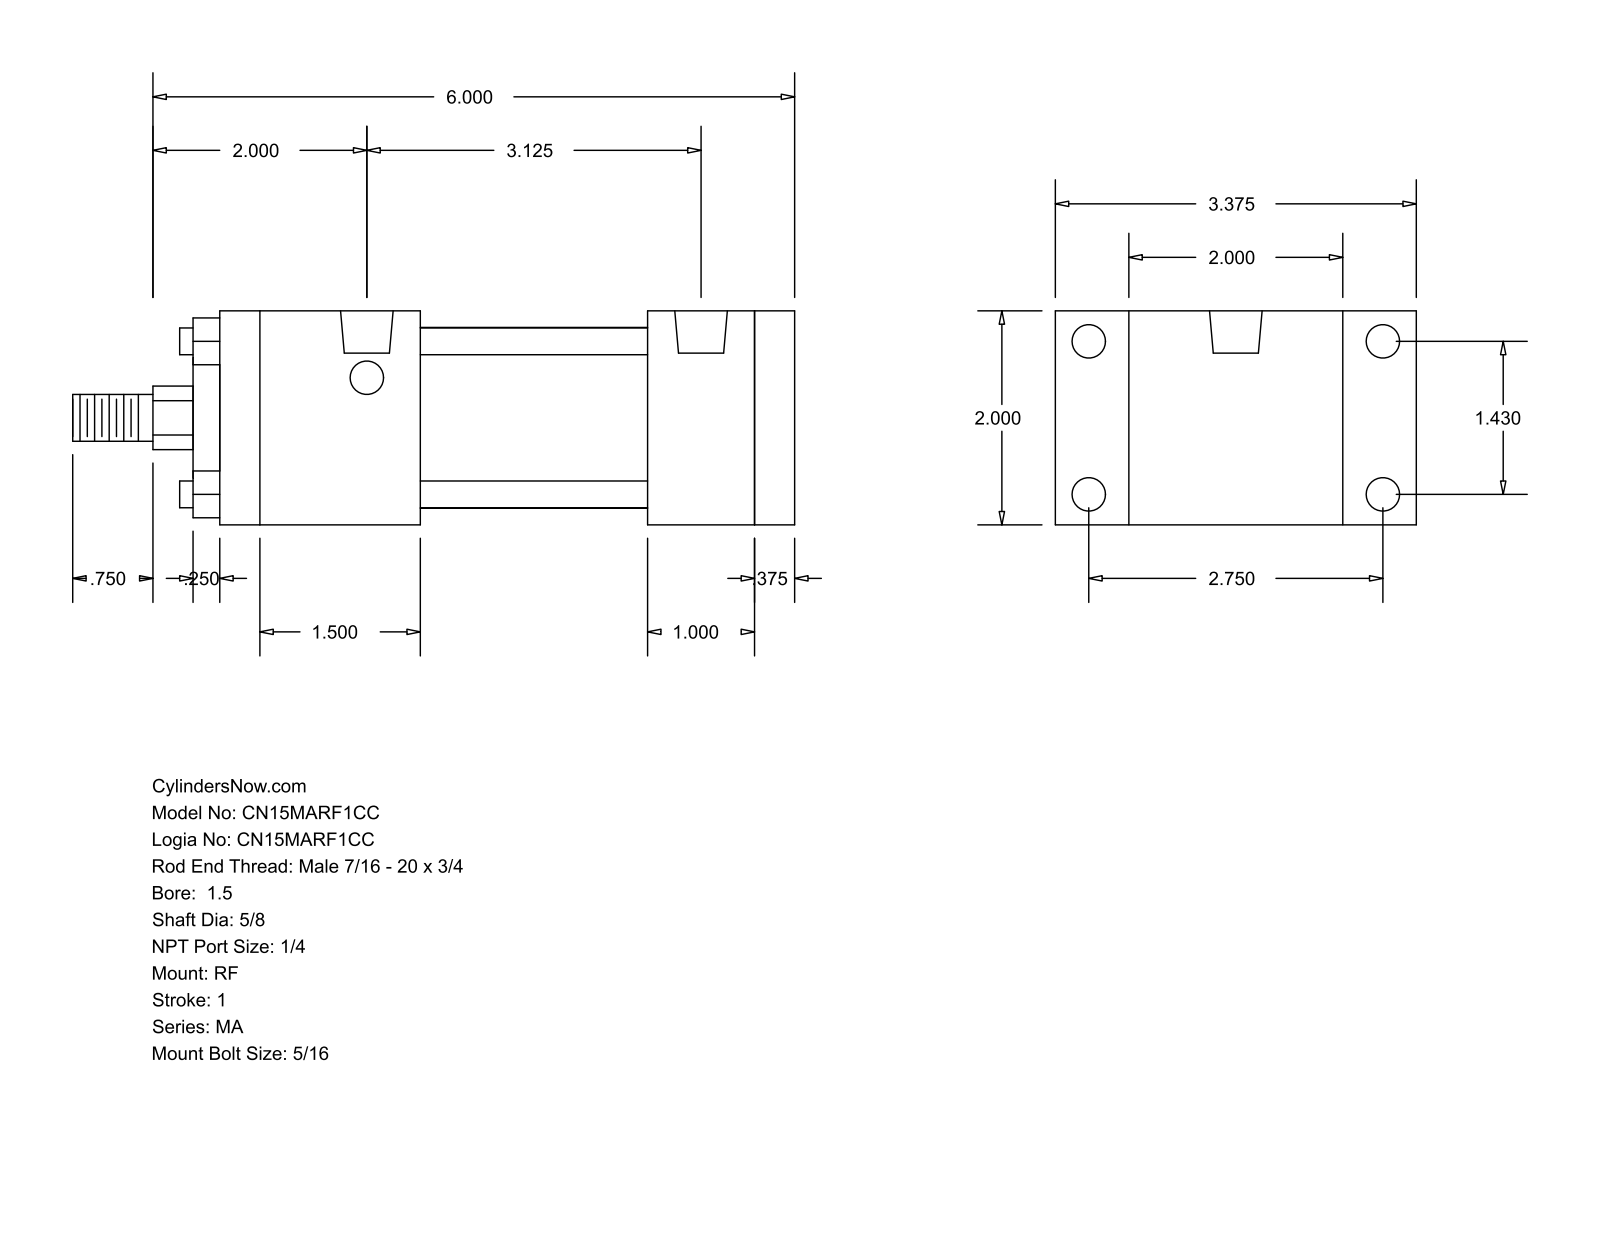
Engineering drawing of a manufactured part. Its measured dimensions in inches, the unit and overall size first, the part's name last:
Units: inches
Overall size (bounding box): 6.75 × 3.375 × 2
Round holes (diameter × count): ⌀0.313 ×8, ⌀0.492 ×2
Round bosses / shafts (diameter × count): ⌀0.25 ×4, ⌀1.69 ×1, ⌀1.125 ×1, ⌀0.625 ×1, ⌀0.437 ×1
Partial cylindrical surfaces — rounded edges, fillets, slot ends (radius × count): R0.297 ×1
Main face-to-face distances: 2, 2.125, 5.375, 0.375, 5, 1.375, 4, 1, 1.875, 3.125
Hole centre spacings: 1.43, 2.75, 3.099, 3.125
Bodies: 0 solids, 92 faces (64 planar, 28 cylindrical, 0 other)
Part name (STEP PRODUCT): MA_RF__0150_0.625
STEP written by: GSSL Pune (CONFIG_CONTROL_DESIGN)
